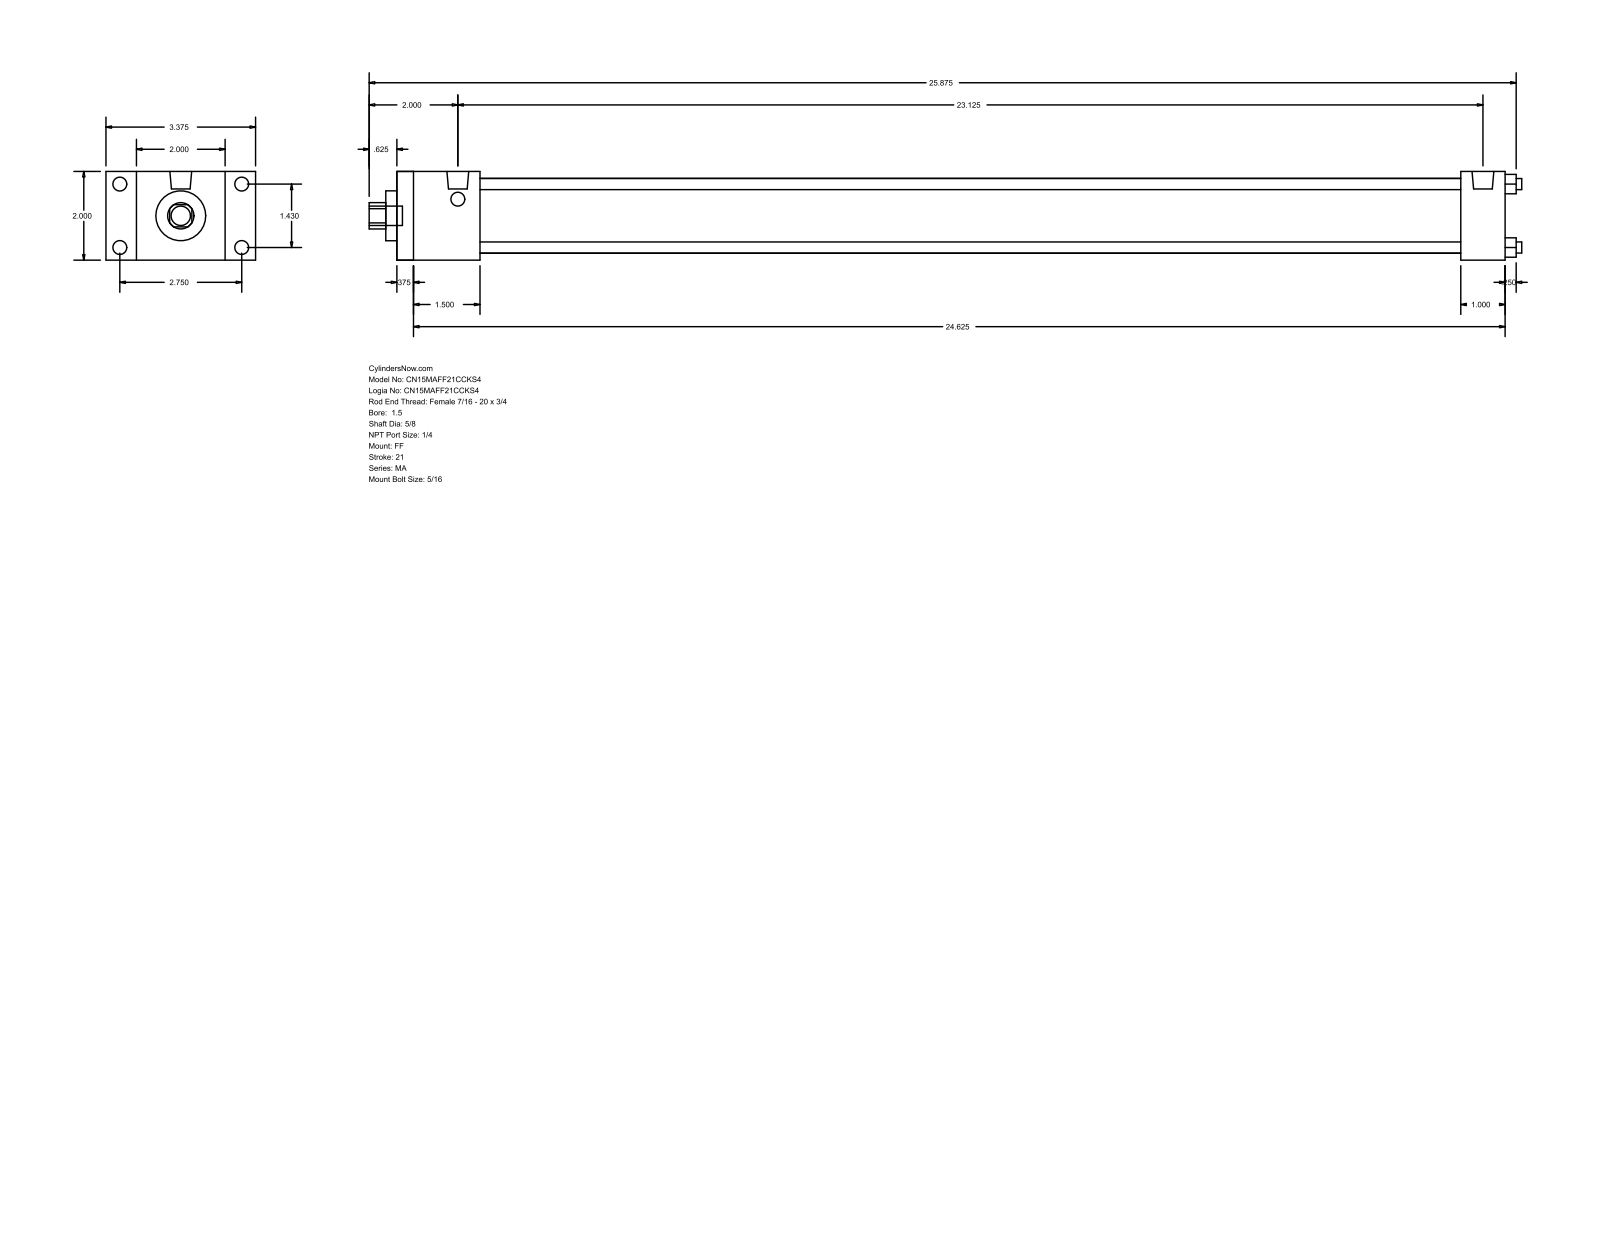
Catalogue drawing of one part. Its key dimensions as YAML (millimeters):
part_name: "MA_FF__0150_0.625"
step_written_by: "GSSL Pune (CONFIG_CONTROL_DESIGN)"
units: millimeters
bodies: {solids: 0, faces: 92, planar: 64, cylindrical: 28, other: 0}
overall_size: [660.4, 85.72, 50.8]
round_holes:
  - {diameter: 6.35, count: 4}
  - {diameter: 15.88, count: 1}
  - {diameter: 28.57, count: 1}
  - {diameter: 42.93, count: 1}
round_bosses_or_shafts:
  - {diameter: 7.94, count: 8}
  - {diameter: 12.49, count: 2}
  - {diameter: 11.11, count: 1}
partial_cylinders:
  - {radius: 7.54, count: 1}
face_to_face_distances: [50.8, 635, 9.52, 625.48, 25.4, 47.62, 609.6, 38.1, 600.08, 561.98]
hole_center_spacings: [25.68, 36.32, 51.36]
